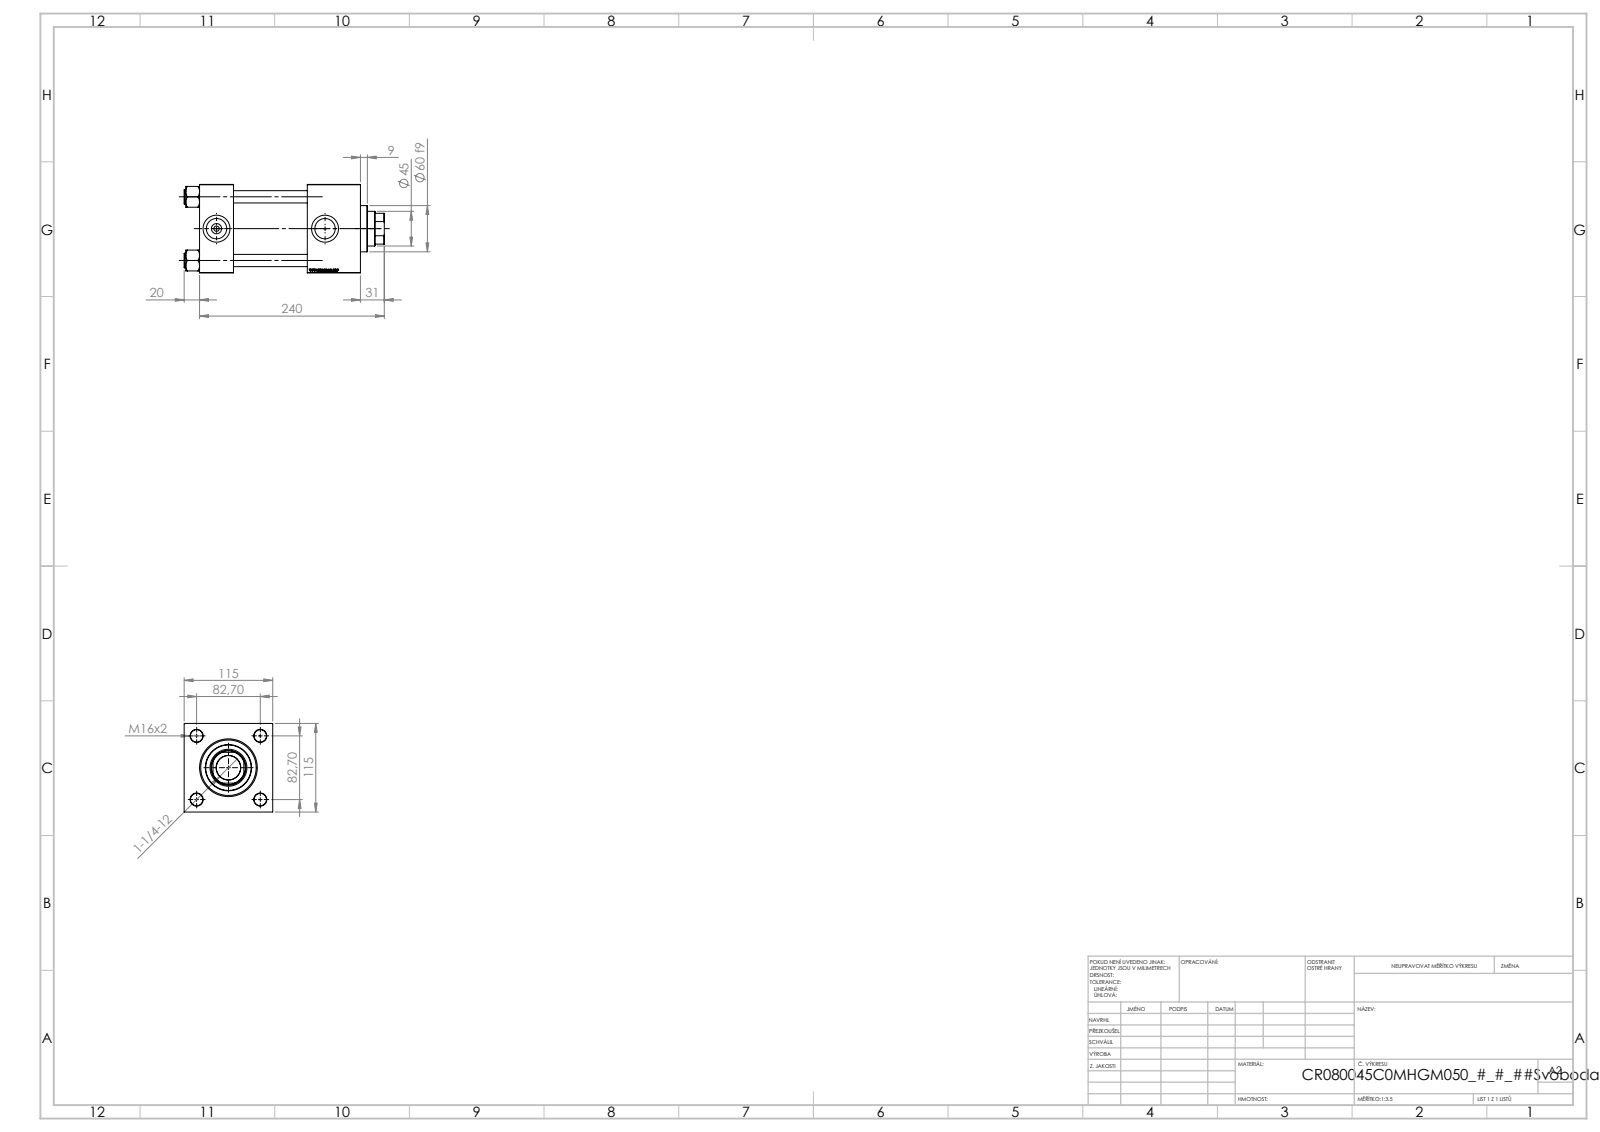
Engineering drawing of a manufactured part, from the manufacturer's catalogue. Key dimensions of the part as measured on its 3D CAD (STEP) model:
Part name (STEP PRODUCT): V215CR_C_Body; NUT_M5_C; V215CR_C_TYCINKA; V215_VC_A (+1 more)
STEP written by: SolidWorks 2019 (CONFIG_CONTROL_DESIGN)
Units: millimetres
Bodies: 11 solids, 1196 faces (574 planar, 86 cylindrical, 536 other)
Overall size (bounding box): 260 × 115 × 115
Volume: 1 915 000 mm³ · Surface area: 299 794 mm²
Round holes (diameter × count): ⌀16 ×4, ⌀7 ×2, ⌀26.44 ×2, ⌀35 ×2, ⌀31.5 ×1, ⌀45 ×1, ⌀48 ×1, ⌀61 ×1, ⌀72 ×1, ⌀80 ×1
Round bosses / shafts (diameter × count): ⌀19 ×4, ⌀86 ×1, ⌀60 ×1
Partial cylindrical surfaces — rounded edges, fillets, slot ends (radius × count): R22 ×1
Main face-to-face distances: 115, 44, 209, 165, 140, 96, 69, 180.3, 136.3, 40.3
Hole centre spacings: 58.48, 82.7, 116.96, 141
